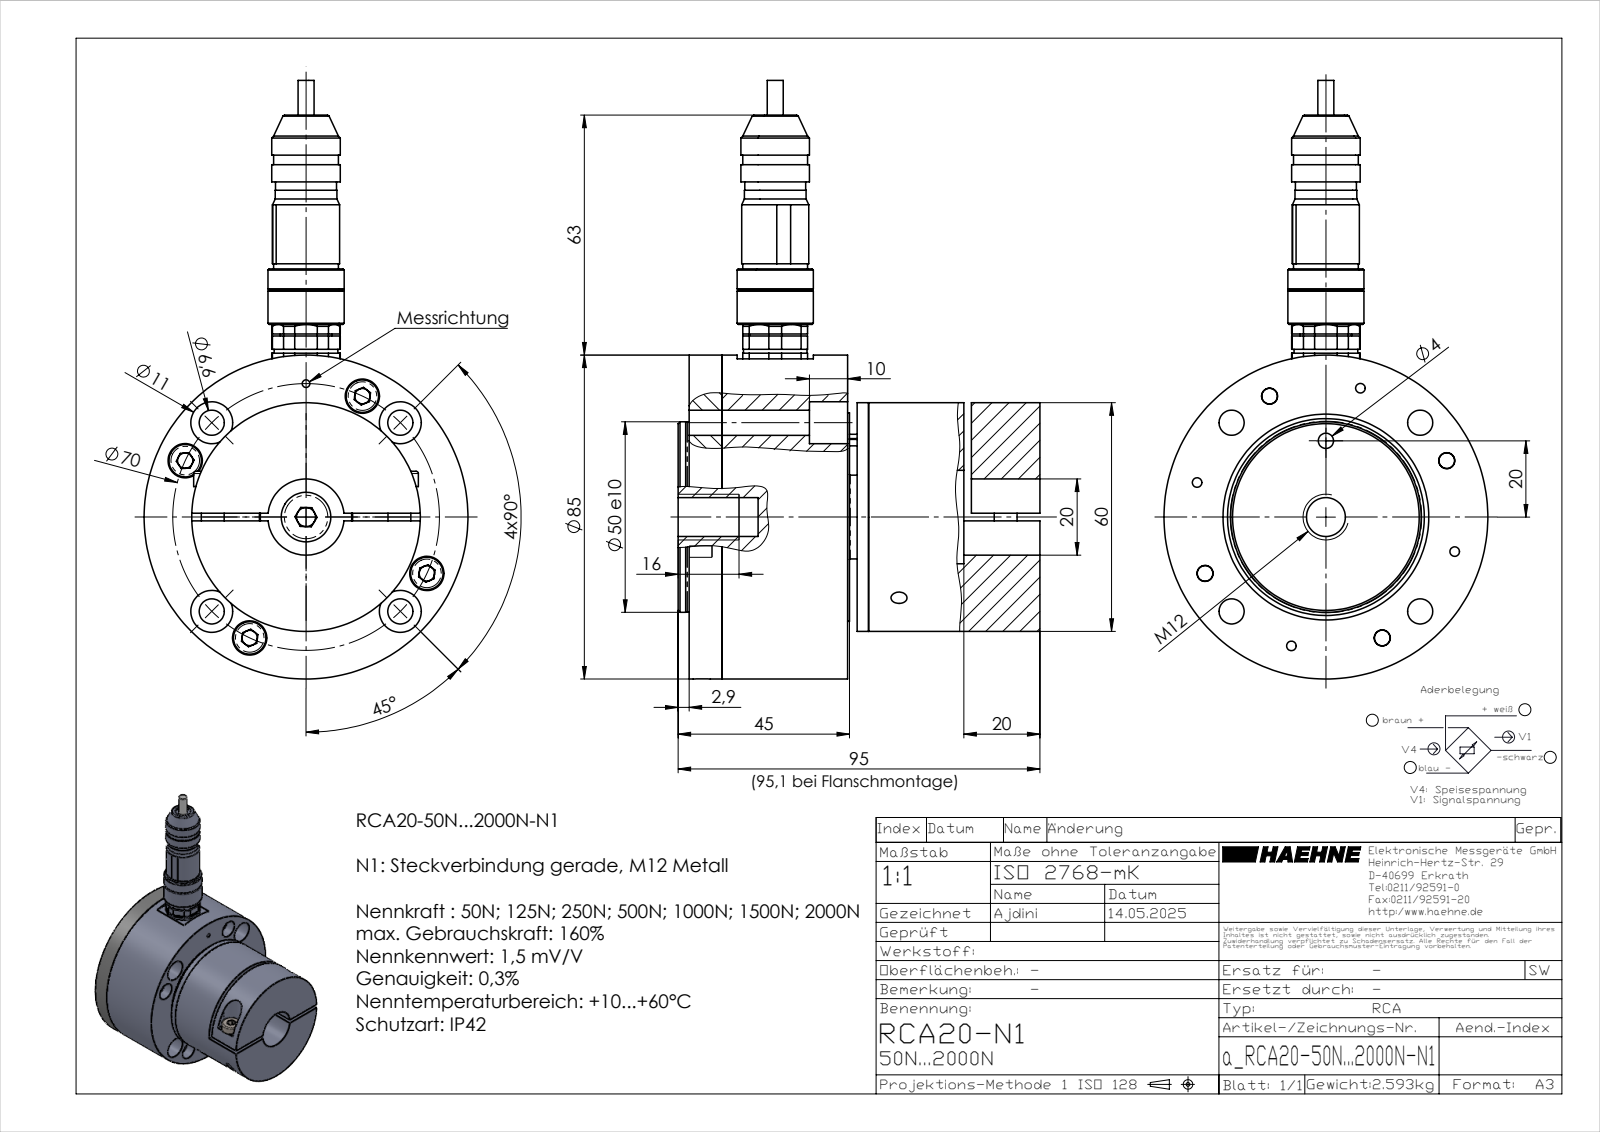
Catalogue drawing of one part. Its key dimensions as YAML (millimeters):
part_name: "inafag_1203-tvh_7zkvytp7yxkimpdvw8sj0b5w4_10; RCA20 Unterteil_30; inafag_1203-tvh_7zkvytp7yxkimpdvw8sj0b5w4_24; inafag_1203-tvh_7zkvytp7yxkimpdvw8sj0b5w4_18 (+8 more)"
step_written_by: "SolidWorks 2023 (AUTOMOTIVE_DESIGN)"
units: millimeters
bodies: {solids: 54, faces: 744, planar: 378, cylindrical: 203, other: 163}
overall_size: [157.06, 95.1, 85]
volume: 376672
surface_area: 114340
round_holes:
  - {diameter: 3.4, count: 9}
  - {diameter: 2.5, count: 8}
  - {diameter: 6.6, count: 6}
  - {diameter: 1, count: 5}
  - {diameter: 4.2, count: 5}
  - {diameter: 4, count: 4}
  - {diameter: 5.3, count: 4}
  - {diameter: 9, count: 4}
  - {diameter: 11, count: 4}
  - {diameter: 4.5, count: 2}
  - {diameter: 5, count: 2}
  - {diameter: 2, count: 1}
round_bosses_or_shafts:
  - {diameter: 3, count: 9}
  - {diameter: 5.7, count: 8}
  - {diameter: 8.5, count: 4}
  - {diameter: 5, count: 4}
  - {diameter: 1.5, count: 4}
  - {diameter: 1, count: 4}
  - {diameter: 17, count: 2}
  - {diameter: 10, count: 2}
partial_cylinders:
  - {radius: 0.3, count: 6}
  - {radius: 1, count: 4}
  - {radius: 5.5, count: 2}
  - {radius: 0.57, count: 1}
  - {radius: 0.6, count: 1}
  - {radius: 0.77, count: 1}
  - {radius: 3.5, count: 1}
face_to_face_distances: [3, 2, 8.6, 47.1, 45, 11.6, 30, 50, 35.5, 38.5]
hole_center_spacings: [35, 49.5, 24.78, 25.2, 32.8, 51.14, 56.46, 2.5]
